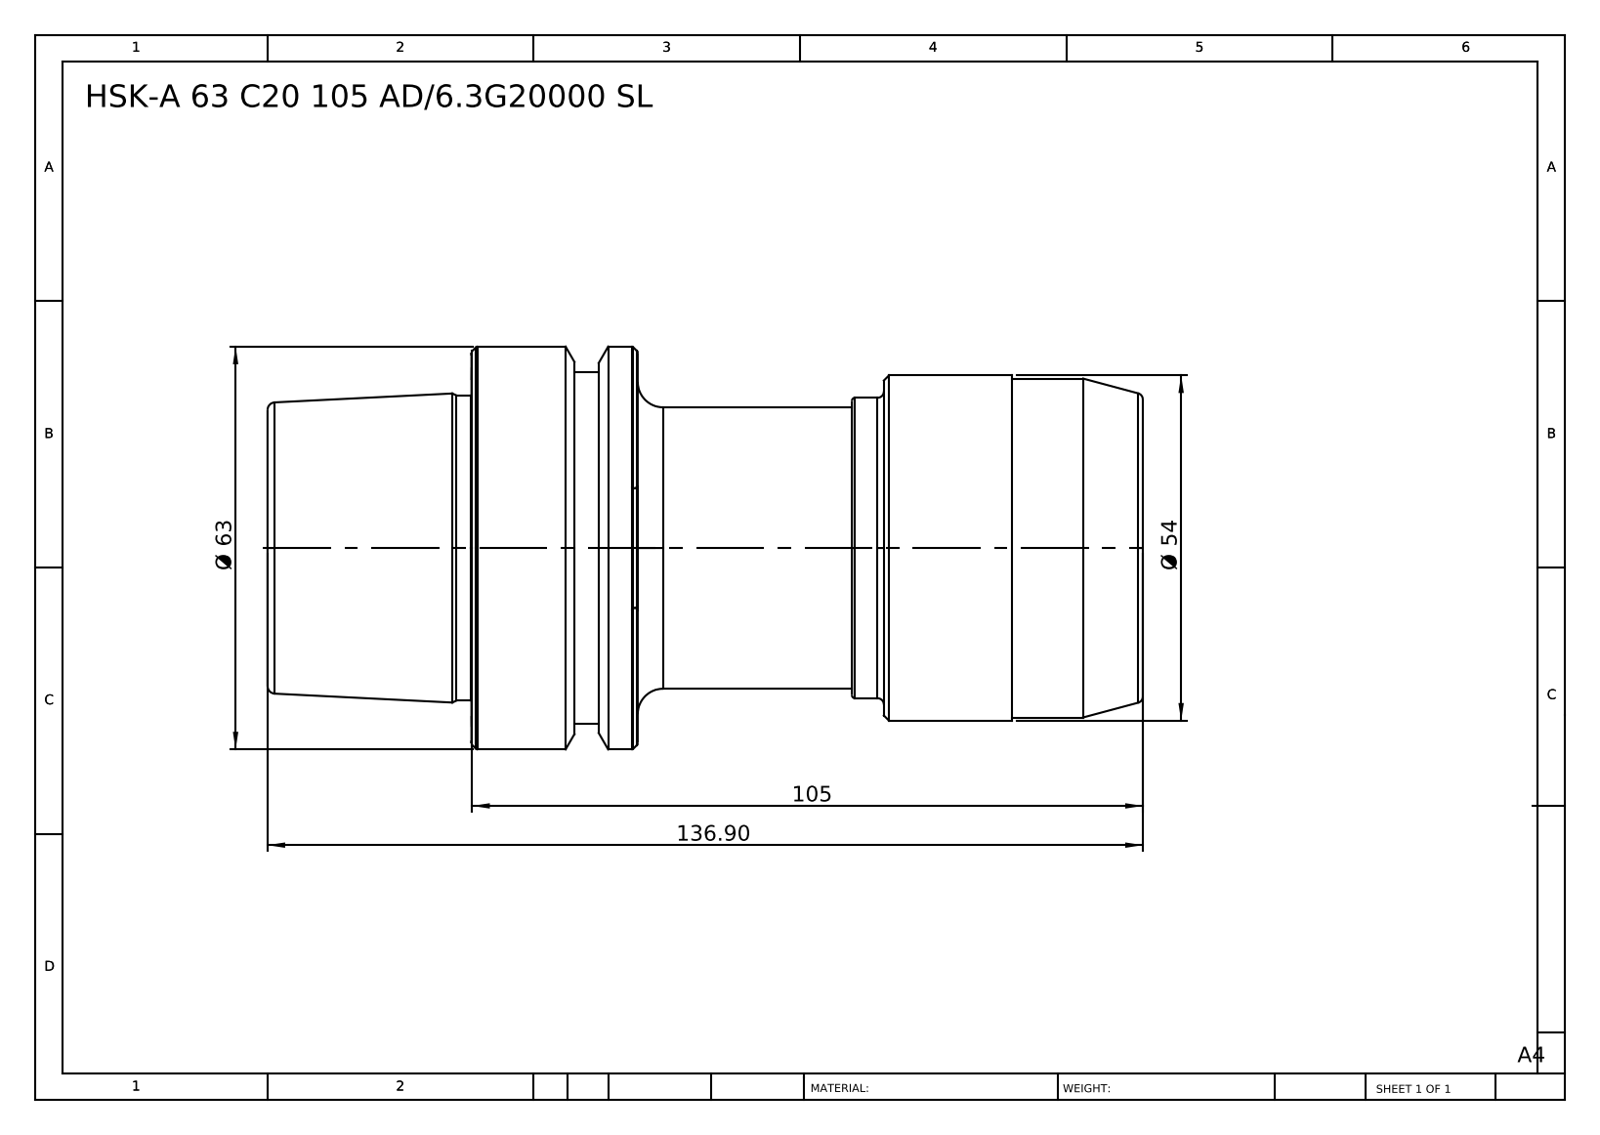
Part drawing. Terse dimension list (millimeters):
name: HSK-A 63 C20 105 AD 6.3G20000 SL
written by: SolidWorks 2014 (CONFIG_CONTROL_DESIGN)
unit: mm
bodies: 1 solid, 78 faces (9 planar, 16 cylindrical, 53 other)
size: 136.9 × 63 × 63
volume: 281 831 mm³; area: 29 521 mm²
bosses: 1× ⌀63, 1× ⌀55, 1× ⌀54, 1× ⌀53, 1× ⌀47.78, 1× ⌀47, 1× ⌀44
face distances: 136.9, 79, 57.9, 105, 26, 31.9, 88.9, 9.9, 16.1, 48
